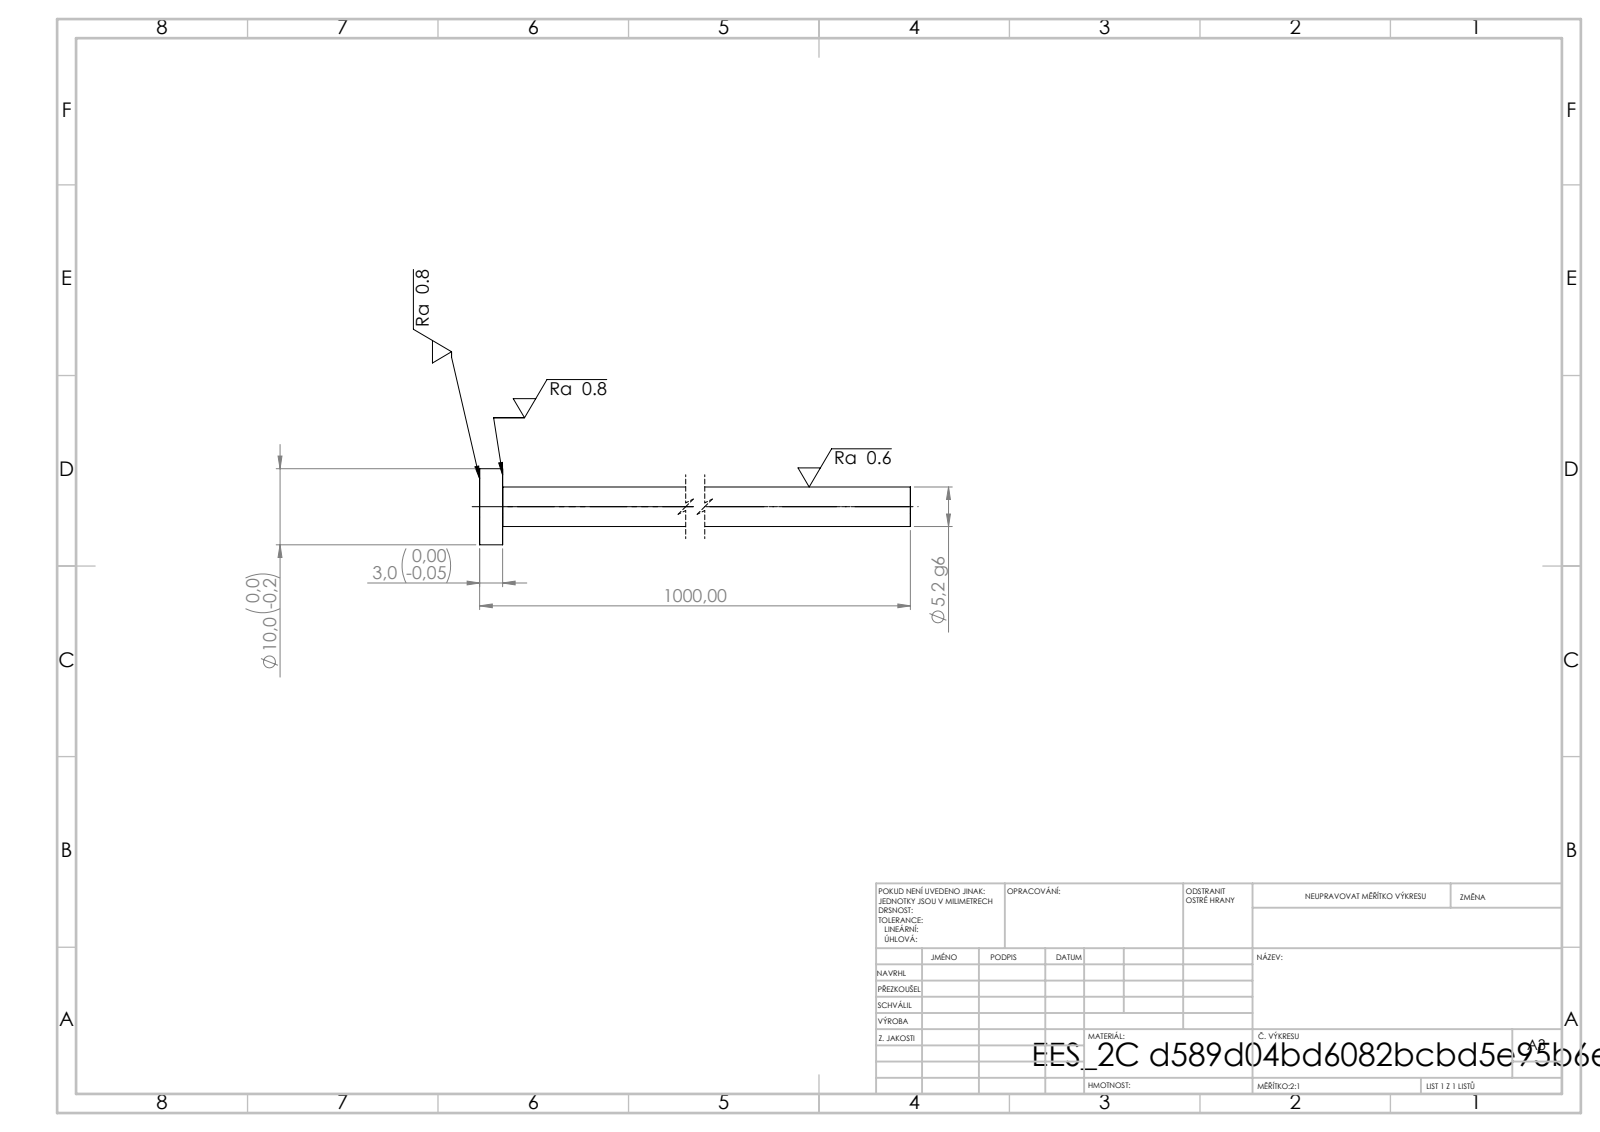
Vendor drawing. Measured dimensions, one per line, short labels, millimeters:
written by: SolidWorks 2019 (CONFIG_CONTROL_DESIGN)
unit: mm
bodies: 1 solid, 7 faces (3 planar, 4 cylindrical, 0 other)
size: 1000 × 10 × 10
volume: 21 409 mm³; area: 16 539 mm²
bosses: 1× ⌀10, 1× ⌀5.2
face distances: 3, 1000, 997
